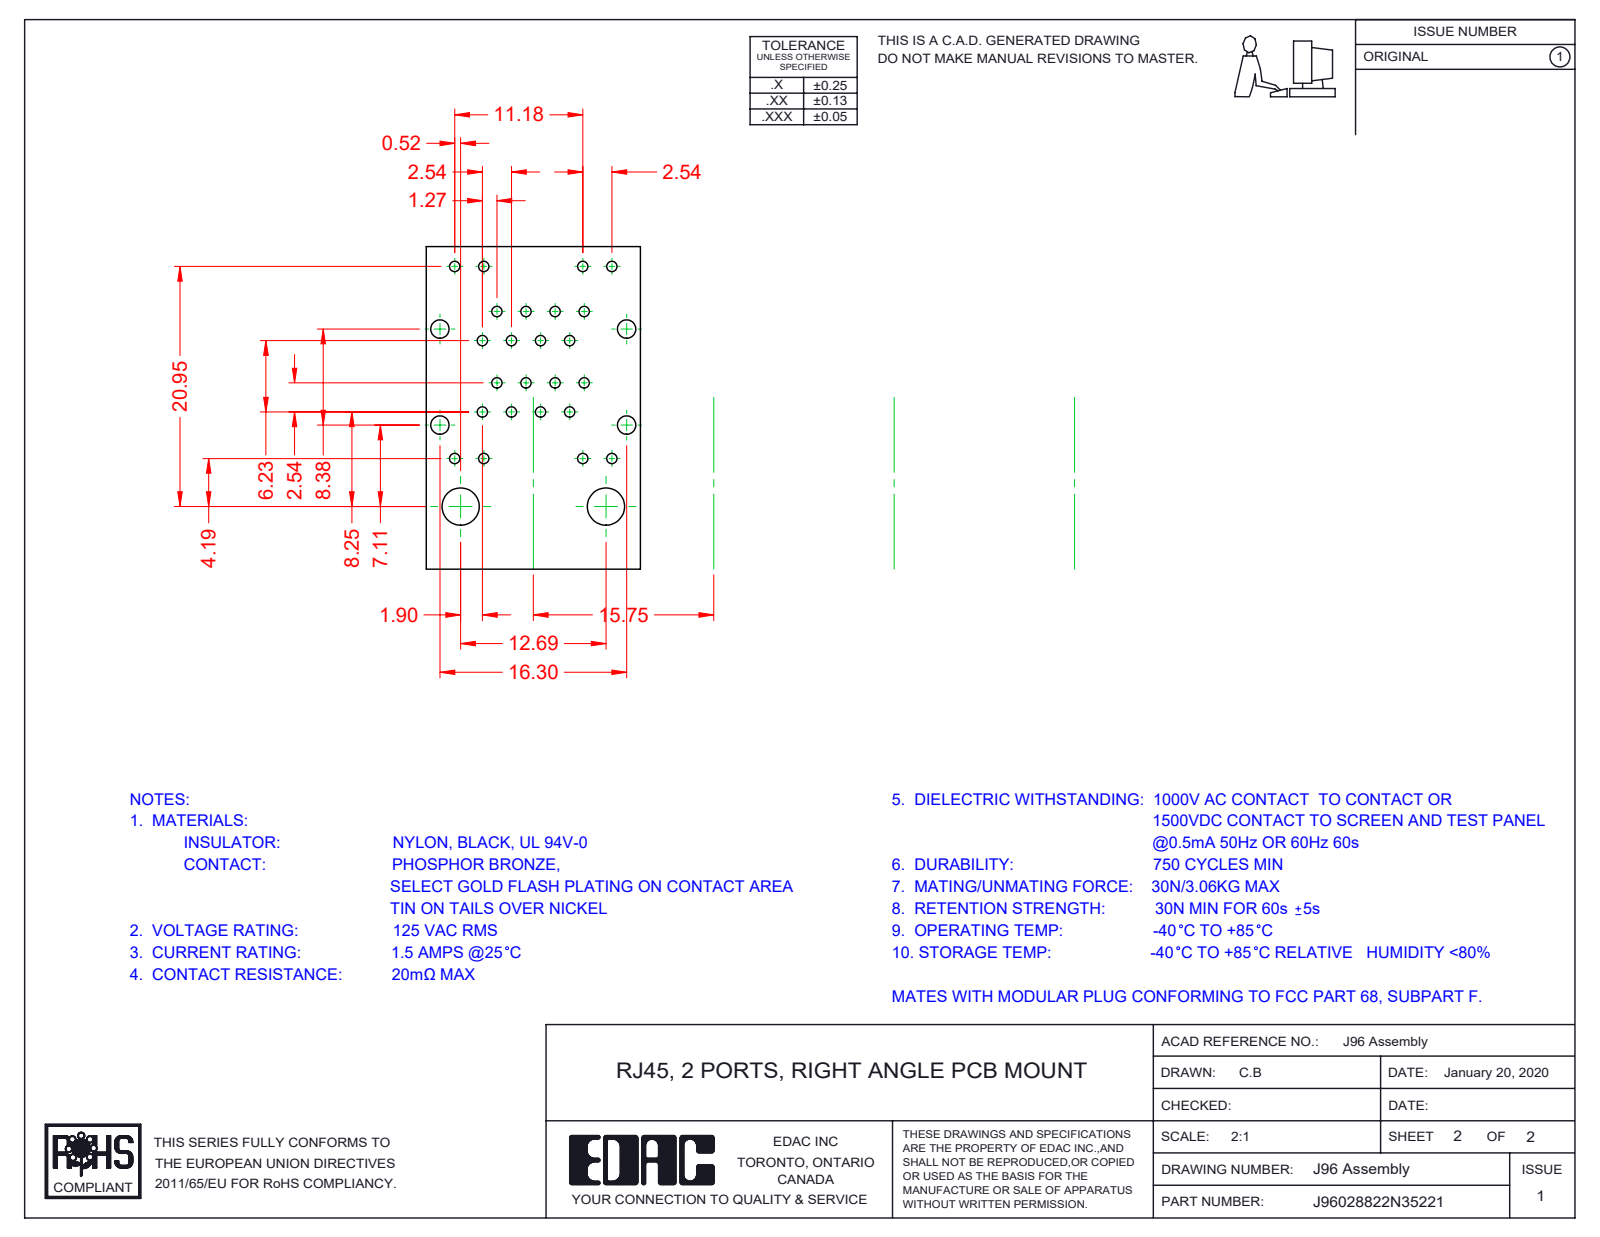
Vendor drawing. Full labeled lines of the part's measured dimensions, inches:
Part name (STEP PRODUCT): 96 Back Plate_2 Ports; 96 Contact Lock Upper; 96 Shield_2 Ports LED - EMI; 96 Contact Lock Lower (+8 more)
STEP written by: SolidWorks 2016 (CONFIG_CONTROL_DESIGN)
Units: inches
Bodies: 27 solids, 2421 faces (1865 planar, 450 cylindrical, 106 other)
Overall size (bounding box): 1.235 × 1.129 × 0.661
Volume: 0.418 in³ · Surface area: 29.6 in²
Partial cylindrical surfaces — rounded edges, fillets, slot ends (radius × count): R0.01 ×48, R0.006 ×32, R0.014 ×24, R0.02 ×16, R0.039 ×16, R0.008 ×14, R0.028 ×9, R0.079 ×5
Main face-to-face distances: 0.642, 0.634, 0.069, 0.65, 0.581, 0.061, 0.573, 0.021, 0.058, 0.441
